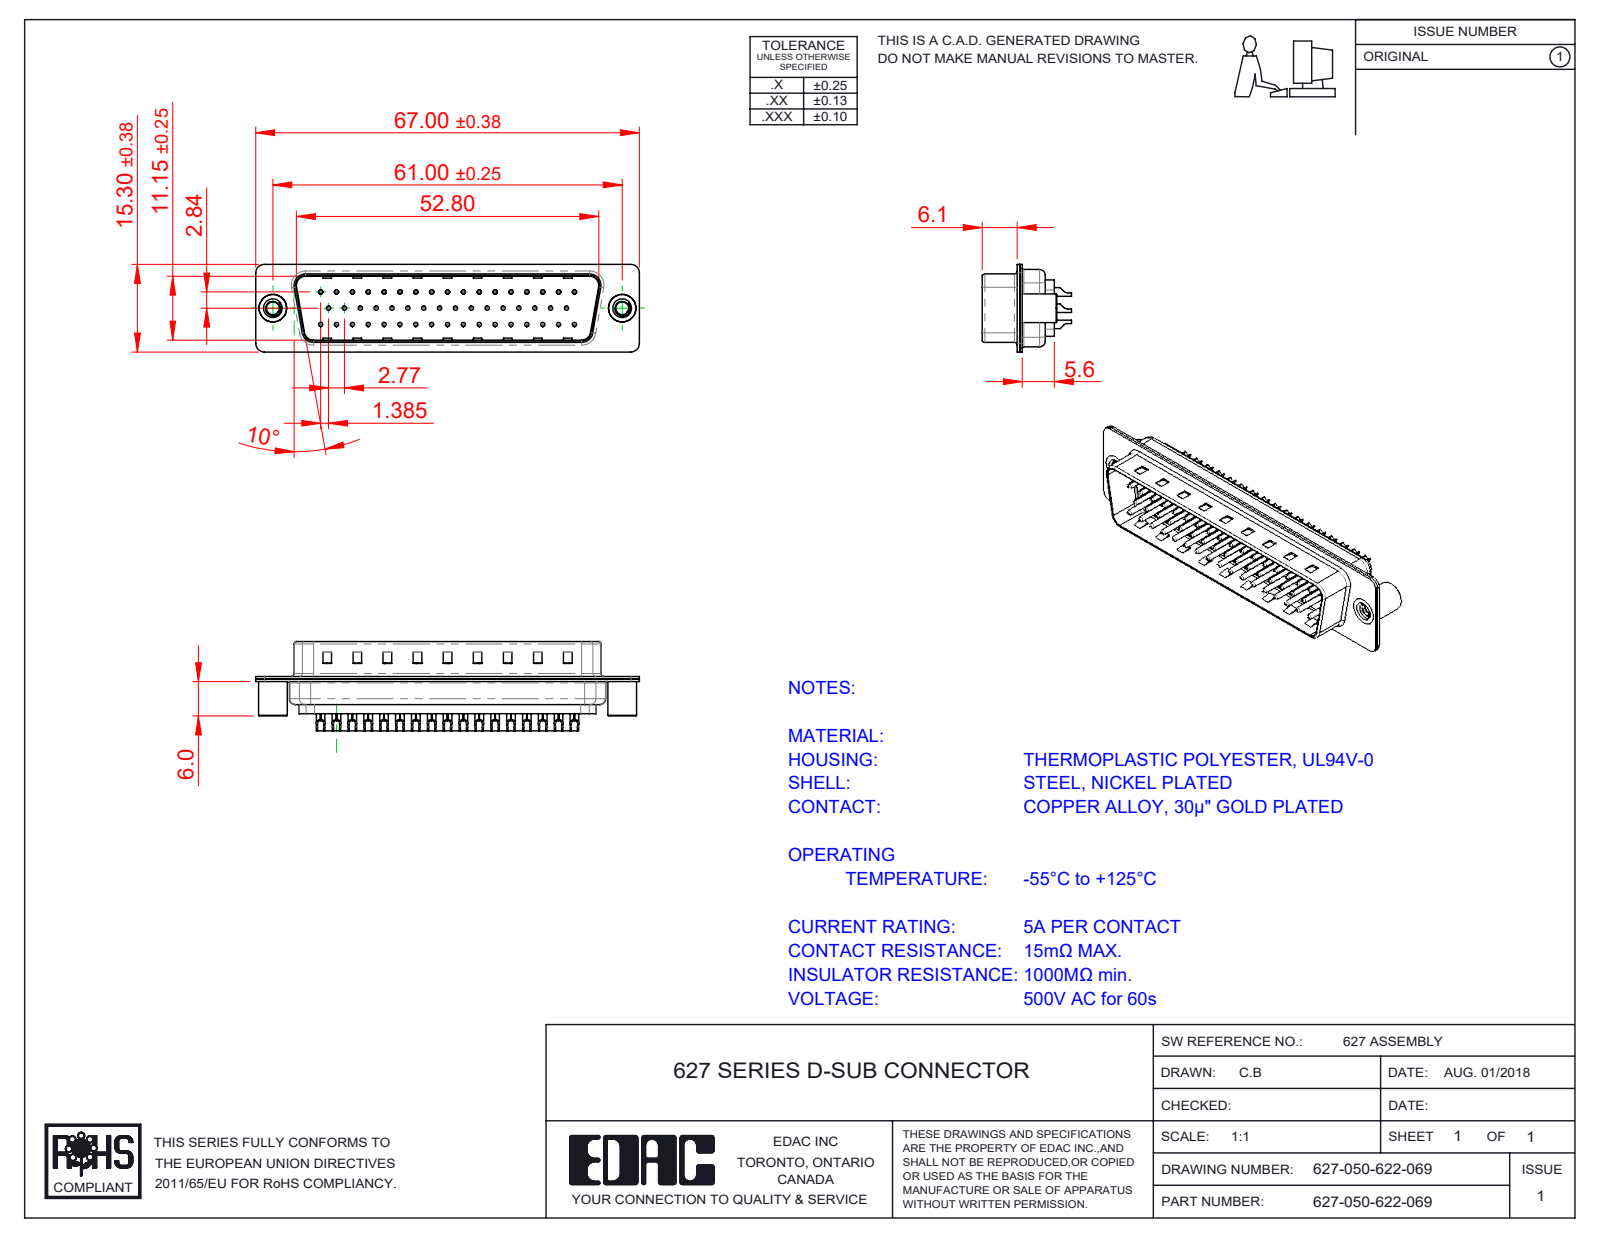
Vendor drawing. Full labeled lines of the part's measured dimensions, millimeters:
Part name (STEP PRODUCT): 627 Shell Rear_50 Contacts; 627-050-622-069; 627 Contact Row 2_22M; 627 Shell Front_50 Contacts (+4 more)
STEP written by: SolidWorks 2020 (CONFIG_CONTROL_DESIGN)
Units: millimetres
Bodies: 55 solids, 3634 faces (903 planar, 1611 cylindrical, 1120 other)
Overall size (bounding box): 67 × 15.6 × 15.3
Volume: 4 548 mm³ · Surface area: 12 964 mm²
Round holes (diameter × count): ⌀1.6 ×58, ⌀0.35 ×50, ⌀1.1 ×50, ⌀0.75 ×8, ⌀2 ×8, ⌀2.26 ×2, ⌀4 ×2, ⌀4.8 ×2
Round bosses / shafts (diameter × count): ⌀2 ×50, ⌀1.5 ×50, ⌀0.75 ×50, ⌀5 ×2, ⌀4.9 ×2
Partial cylindrical surfaces — rounded edges, fillets, slot ends (radius × count): R1.5 ×16, R2 ×12, R0.5 ×8, R1.6 ×8, R1 ×7, R0.25 ×4, R0.6 ×4, R0.65 ×4
Main face-to-face distances: 0.4, 0.45, 11.55, 0.9, 6.05, 6.5, 0.78, 1.95, 0.77, 12.33
Hole centre spacings: 2.77, 3.16, 5.54, 8.31, 11.08, 13.85, 16.62, 19.39
